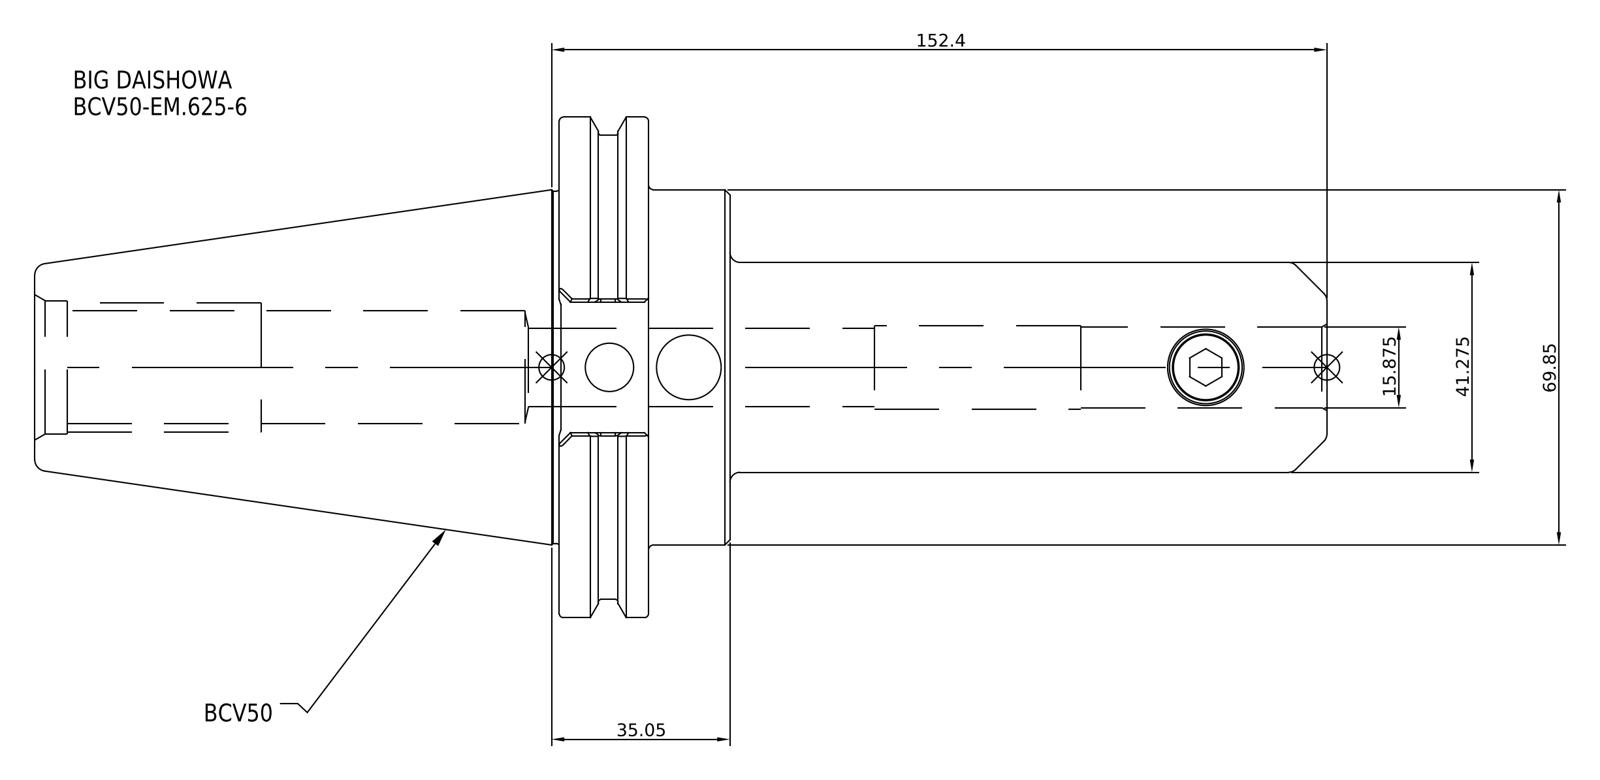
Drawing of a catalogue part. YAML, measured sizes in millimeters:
part_name: "BCV50-EM_625-6"
step_written_by: "SolidWorks 2021 (CONFIG_CONTROL_DESIGN)"
units: millimeters
bodies: {solids: 1, faces: 30, planar: 8, cylindrical: 14, other: 8}
overall_size: [254, 98.43, 98.43]
volume: 573890
surface_area: 61490
round_holes:
  - {diameter: 15.88, count: 1}
round_bosses_or_shafts:
  - {diameter: 98.43, count: 1}
  - {diameter: 91.29, count: 1}
  - {diameter: 69.85, count: 1}
  - {diameter: 41.28, count: 1}
face_to_face_distances: [17.55, 16, 33.55, 136.65, 120.65, 103.1, 117.35, 133.35, 150.9, 254]
